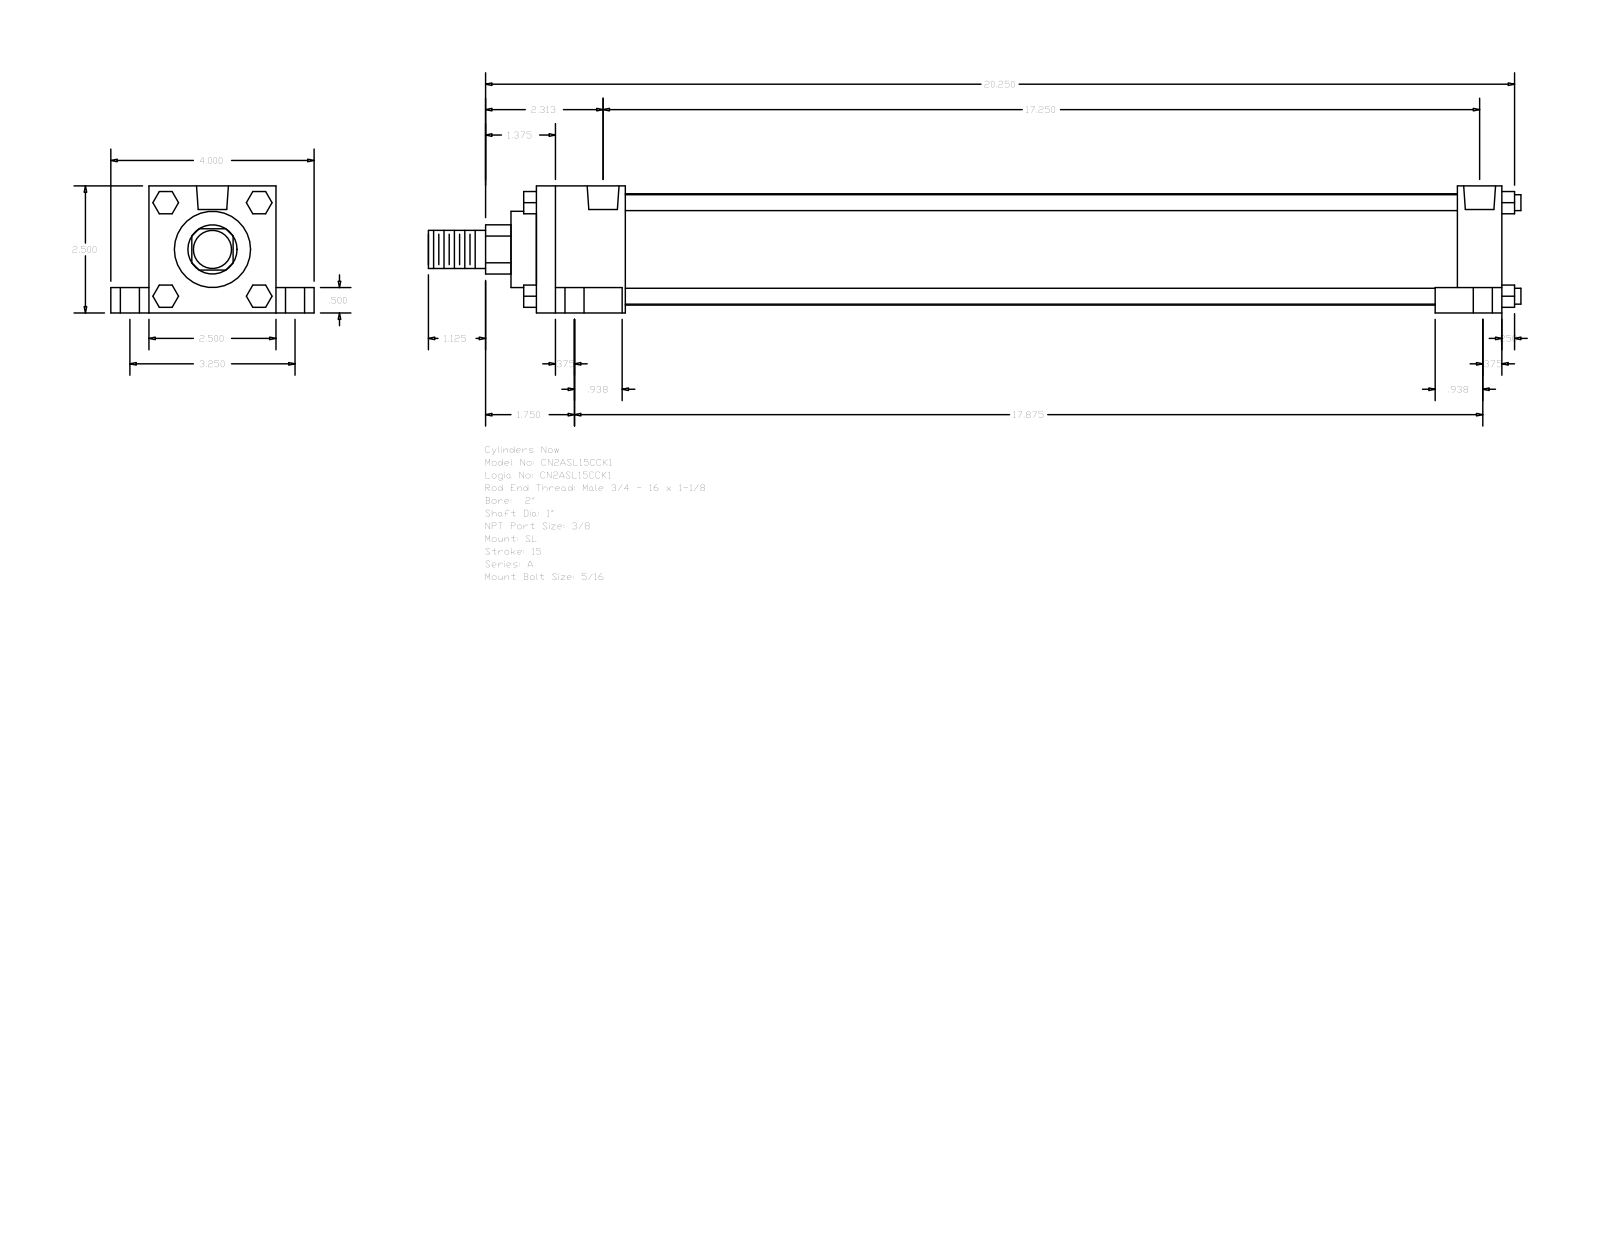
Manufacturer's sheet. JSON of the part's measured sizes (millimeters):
{"part_name": "A_SL__0200_1", "step_written_by": "GSSL Pune (CONFIG_CONTROL_DESIGN)", "units": "millimeters", "bodies": {"solids": 0, "faces": 148, "planar": 112, "cylindrical": 36, "other": 0}, "overall_size": [546.1, 101.6, 63.5], "round_holes": [[5.56, 4], [9.53, 4], [15.88, 4], [15.93, 2]], "round_bosses_or_shafts": [[7.94, 4], [55.63, 1], [38.1, 1], [25.4, 1], [19.05, 1]], "partial_cylinders_radius": [[12.29, 1]], "face_to_face_distances": [63.5, 482.6, 12.7, 50.8, 19.05, 82.55, 44.45, 438.15, 460.37, 415.92], "hole_center_spacings": [41.3, 41.64, 43.67, 44.22, 82.54, 432.58, 440.09, 441.67]}
